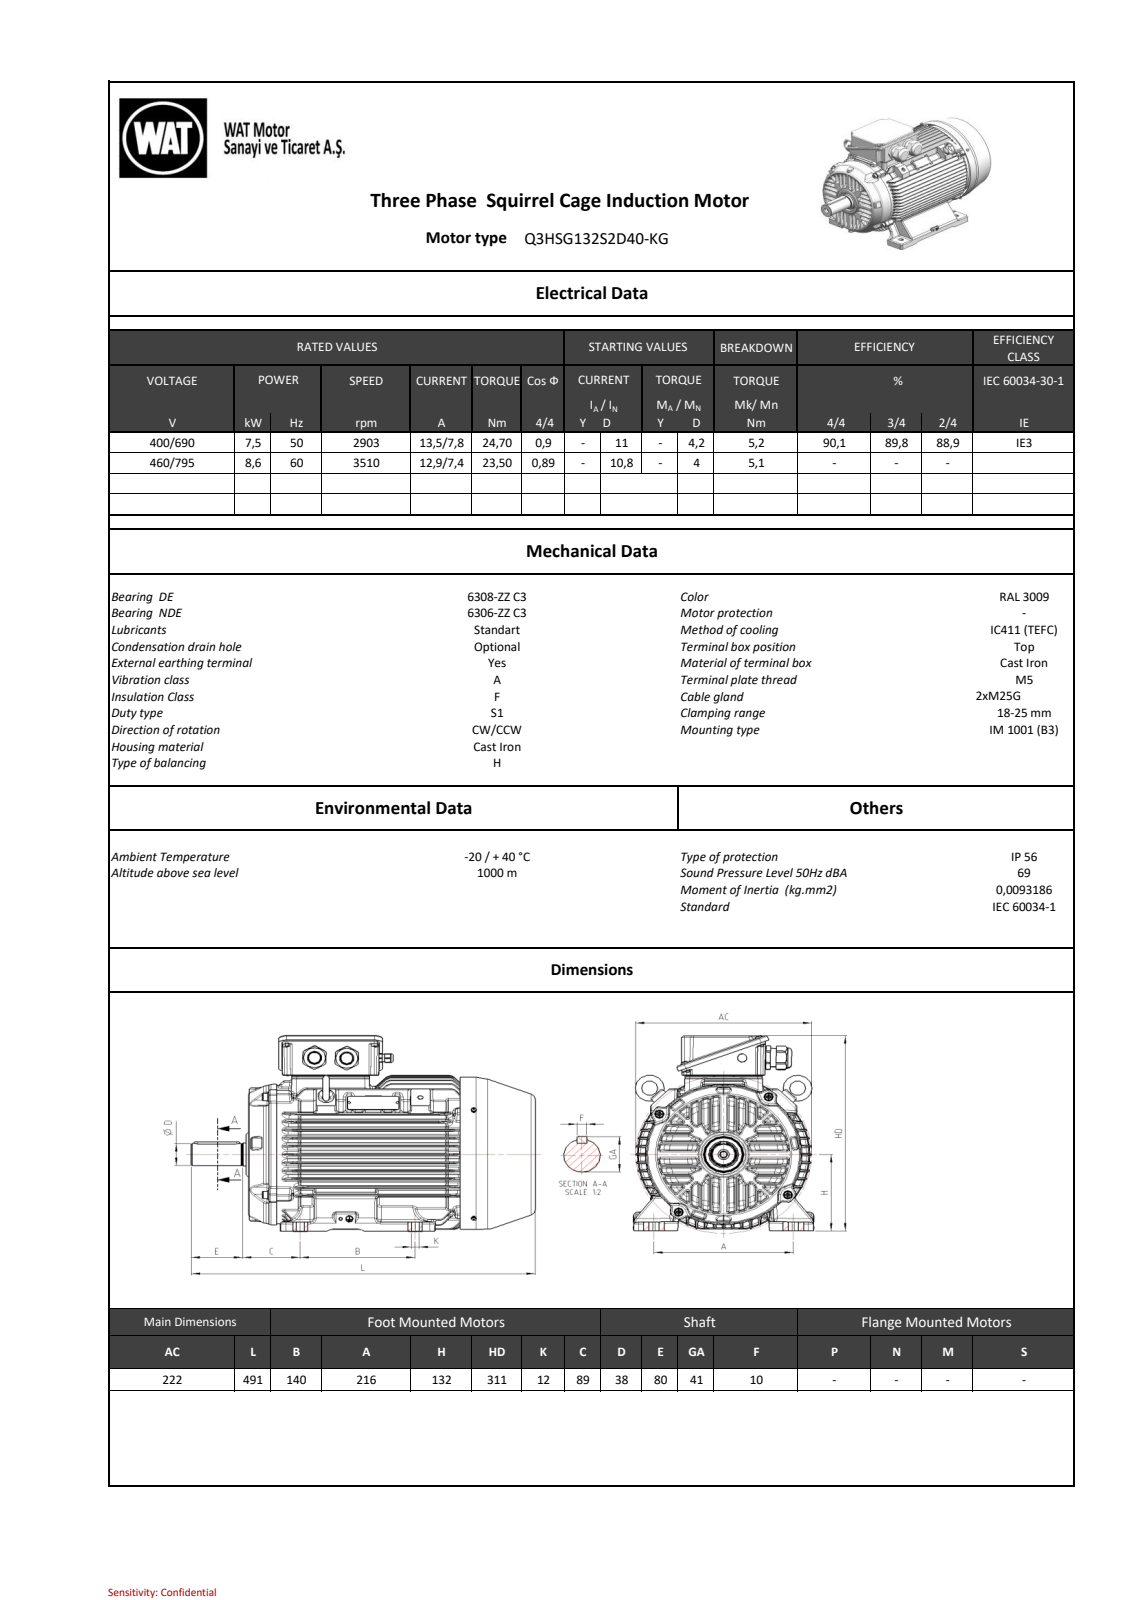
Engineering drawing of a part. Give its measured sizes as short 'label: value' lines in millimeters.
name: 260021E4F5C7p84o
written by: SIEMENS PLM Software NX 11.0 (AUTOMOTIVE_DESIGN)
unit: mm
bodies: 0 solids, 5593 faces (1060 planar, 1534 cylindrical, 2999 other)
size: 491 × 311.13 × 275
holes: 9× ⌀5, 2× ⌀2.5, 2× ⌀6.8, 2× ⌀10, 2× ⌀17.2, 1× ⌀6, 1× ⌀6.3, 1× ⌀8, 1× ⌀10.2, 1× ⌀11.3, 1× ⌀13, 1× ⌀24.5
bosses: 4× ⌀12, 4× ⌀10, 4× ⌀8.65, 4× ⌀8, 4× ⌀4, 2× ⌀27.7, 2× ⌀25.25, 2× ⌀20
rounds: 320× R4, 118× R0.5, 118× R3, 96× R1.5, 45× R2, 41× R1, 28× R6, 26× R0.25
face distances: 13.1, 13.18, 26.28, 39.54, 26.44, 13.26, 90.54, 52.86, 39.76, 26.58
hole spacings: 97, 137.18, 33.69, 111.28, 158.92, 191.06, 194.01, 27.5
